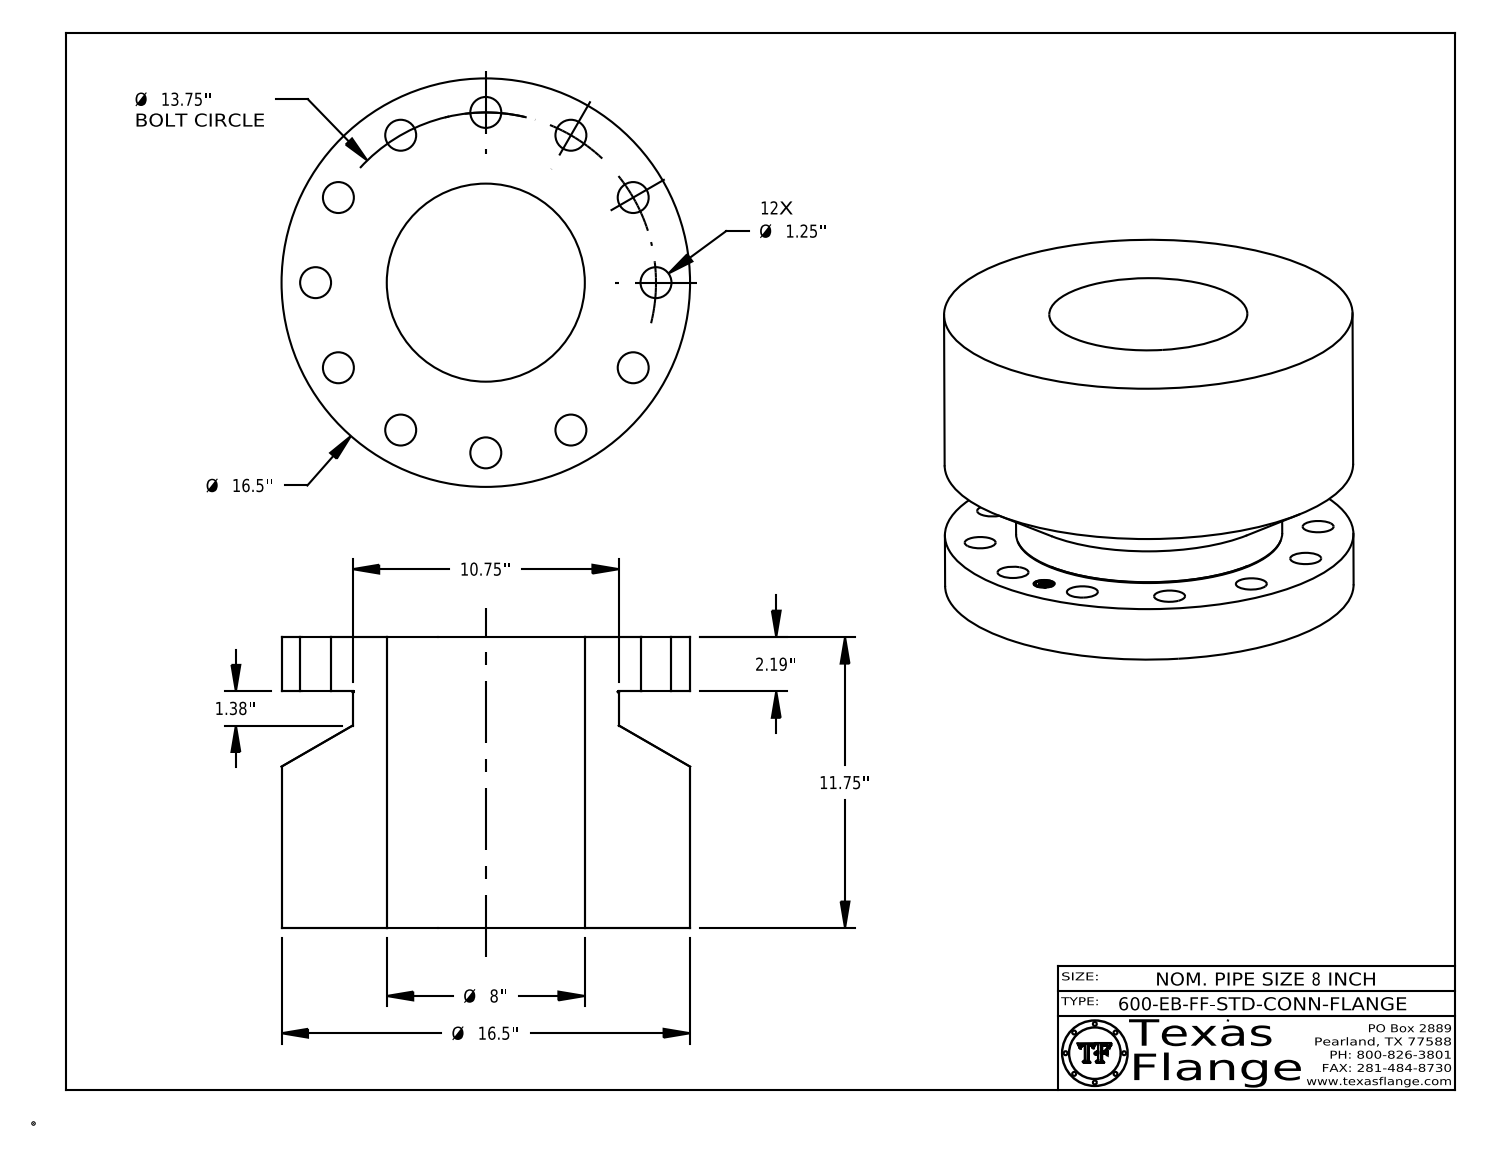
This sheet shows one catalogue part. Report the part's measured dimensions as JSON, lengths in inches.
{"part_name": "8-600-EB-FF-STD-CONN-FLANGE", "step_written_by": "CATIA V5 STEP AP214 (AUTOMOTIVE_DESIGN)", "units": "inches", "bodies": {"solids": 1, "faces": 426, "planar": 368, "cylindrical": 52, "other": 6}, "overall_size": [16.5, 16.5, 11.75], "volume_in3": 1610, "surface_area_in2": 1461, "round_holes": [[1.25, 12], [0.85, 1], [8, 1]], "round_bosses_or_shafts": [[0.051, 8], [16.5, 1], [10.75, 1], [0.67, 1]], "face_to_face_distances": [11.75, 2.19, 9.56, 2.185, 9.565, 0.254, 0.248, 0.046, 0.165, 0.211], "hole_center_spacings": [6.875, 6.875, 9.723, 11.908, 13.281, 3.559, 3.559, 13.75]}
